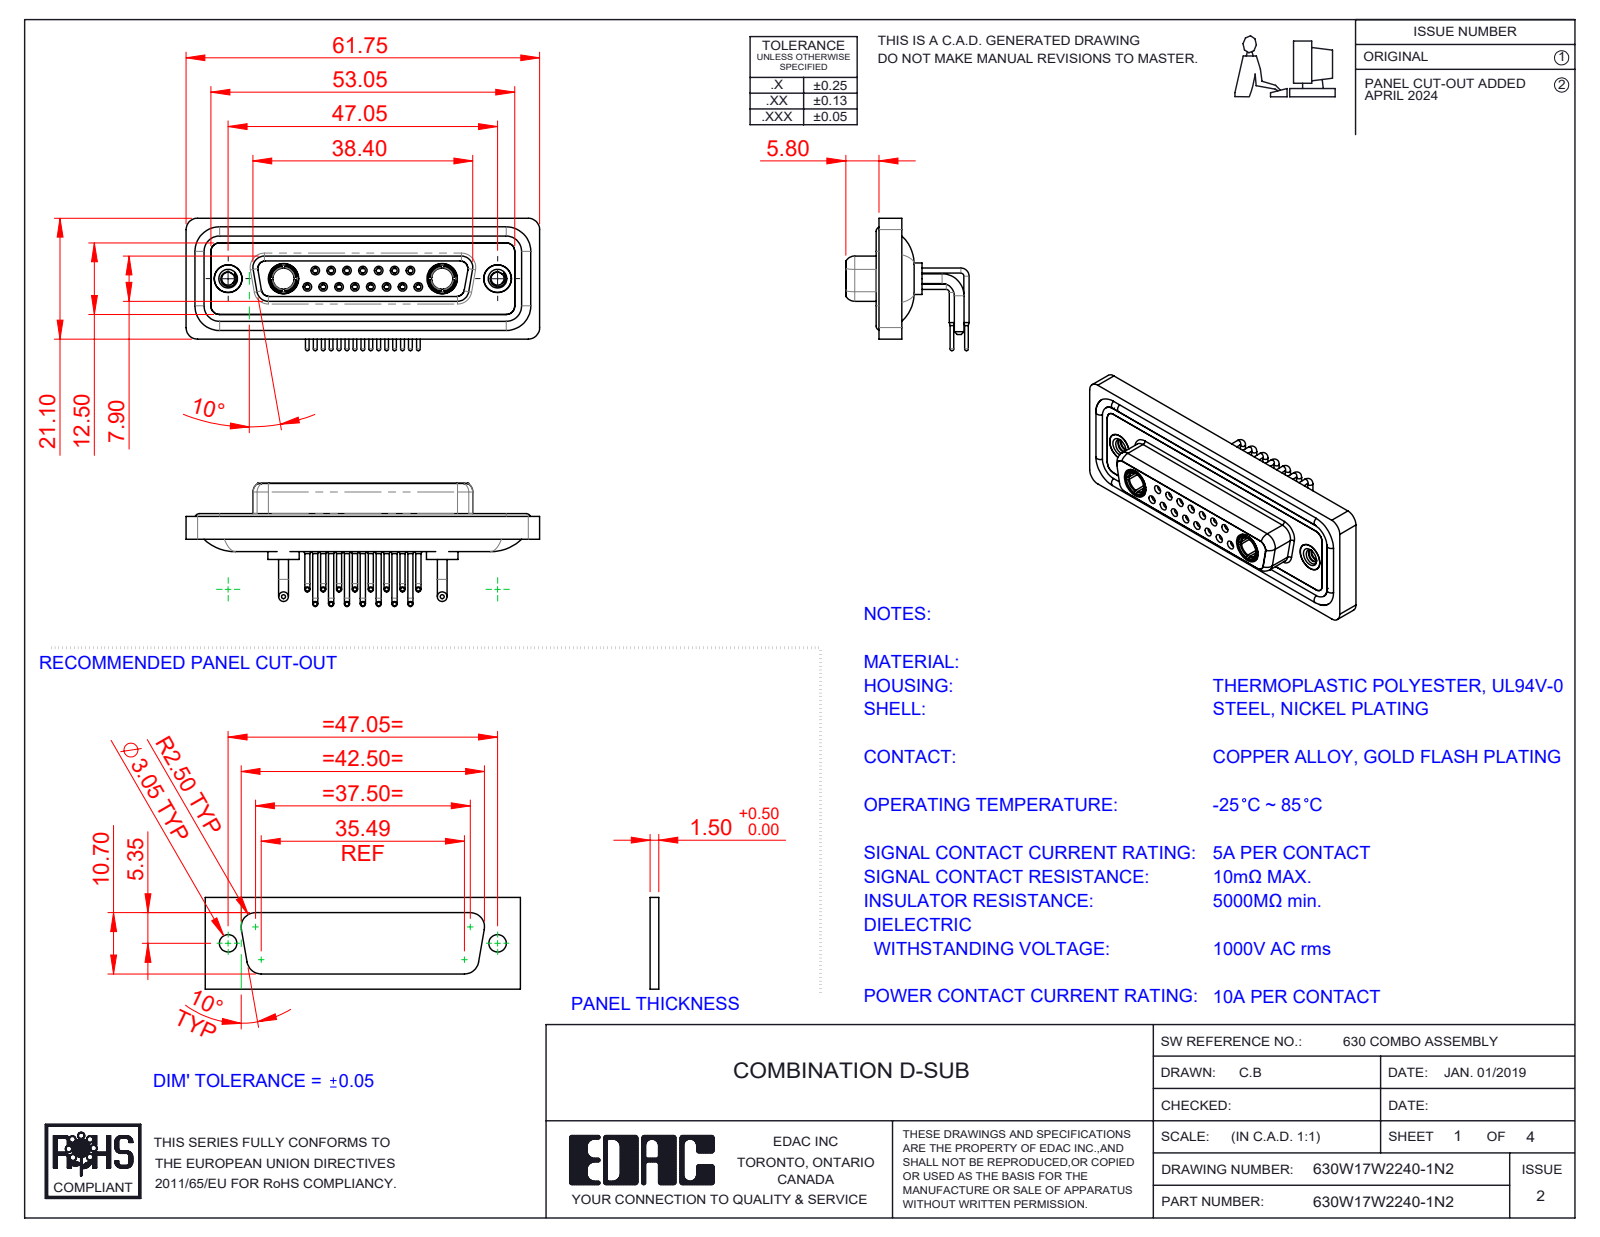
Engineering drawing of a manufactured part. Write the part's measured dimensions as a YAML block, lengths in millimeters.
part_name: "630Combo Contact Row 2_50 Contacts; 630Combo Threaded Rivet_2; 630Combo Shell Rear_25 Contacts; 630Combo Shell Front_25 Contacts (+5 more)"
step_written_by: "SolidWorks 2023 (CONFIG_CONTROL_DESIGN)"
units: millimeters
bodies: {solids: 26, faces: 1337, planar: 388, cylindrical: 583, other: 366}
overall_size: [61.75, 23.12, 21.53]
volume: 8371
surface_area: 14429
round_holes:
  - {diameter: 0.9, count: 15}
  - {diameter: 1.1, count: 15}
  - {diameter: 1.5, count: 15}
  - {diameter: 2, count: 15}
  - {diameter: 1.6, count: 8}
  - {diameter: 1.7, count: 7}
  - {diameter: 4.85, count: 4}
  - {diameter: 2.26, count: 2}
  - {diameter: 3.7, count: 2}
  - {diameter: 4, count: 2}
  - {diameter: 4.05, count: 2}
  - {diameter: 5, count: 2}
round_bosses_or_shafts:
  - {diameter: 0.9, count: 15}
  - {diameter: 0.65, count: 15}
  - {diameter: 1.6, count: 11}
  - {diameter: 1.7, count: 4}
  - {diameter: 5.5, count: 2}
  - {diameter: 5.2, count: 2}
  - {diameter: 4.96, count: 2}
  - {diameter: 4.95, count: 2}
partial_cylinders:
  - {radius: 1.5, count: 18}
  - {radius: 2, count: 18}
  - {radius: 1.35, count: 8}
  - {radius: 1.6, count: 8}
  - {radius: 0.25, count: 4}
  - {radius: 0.5, count: 4}
  - {radius: 0.6, count: 4}
  - {radius: 0.65, count: 4}
face_to_face_distances: [0.4, 1.8, 4.1, 1.1, 1.6, 1.5, 3.1, 2.5, 3.7, 1.4]
hole_center_spacings: [3.16, 2.77, 5.54, 8.31, 5.04, 7.49, 11.08, 5.03]
